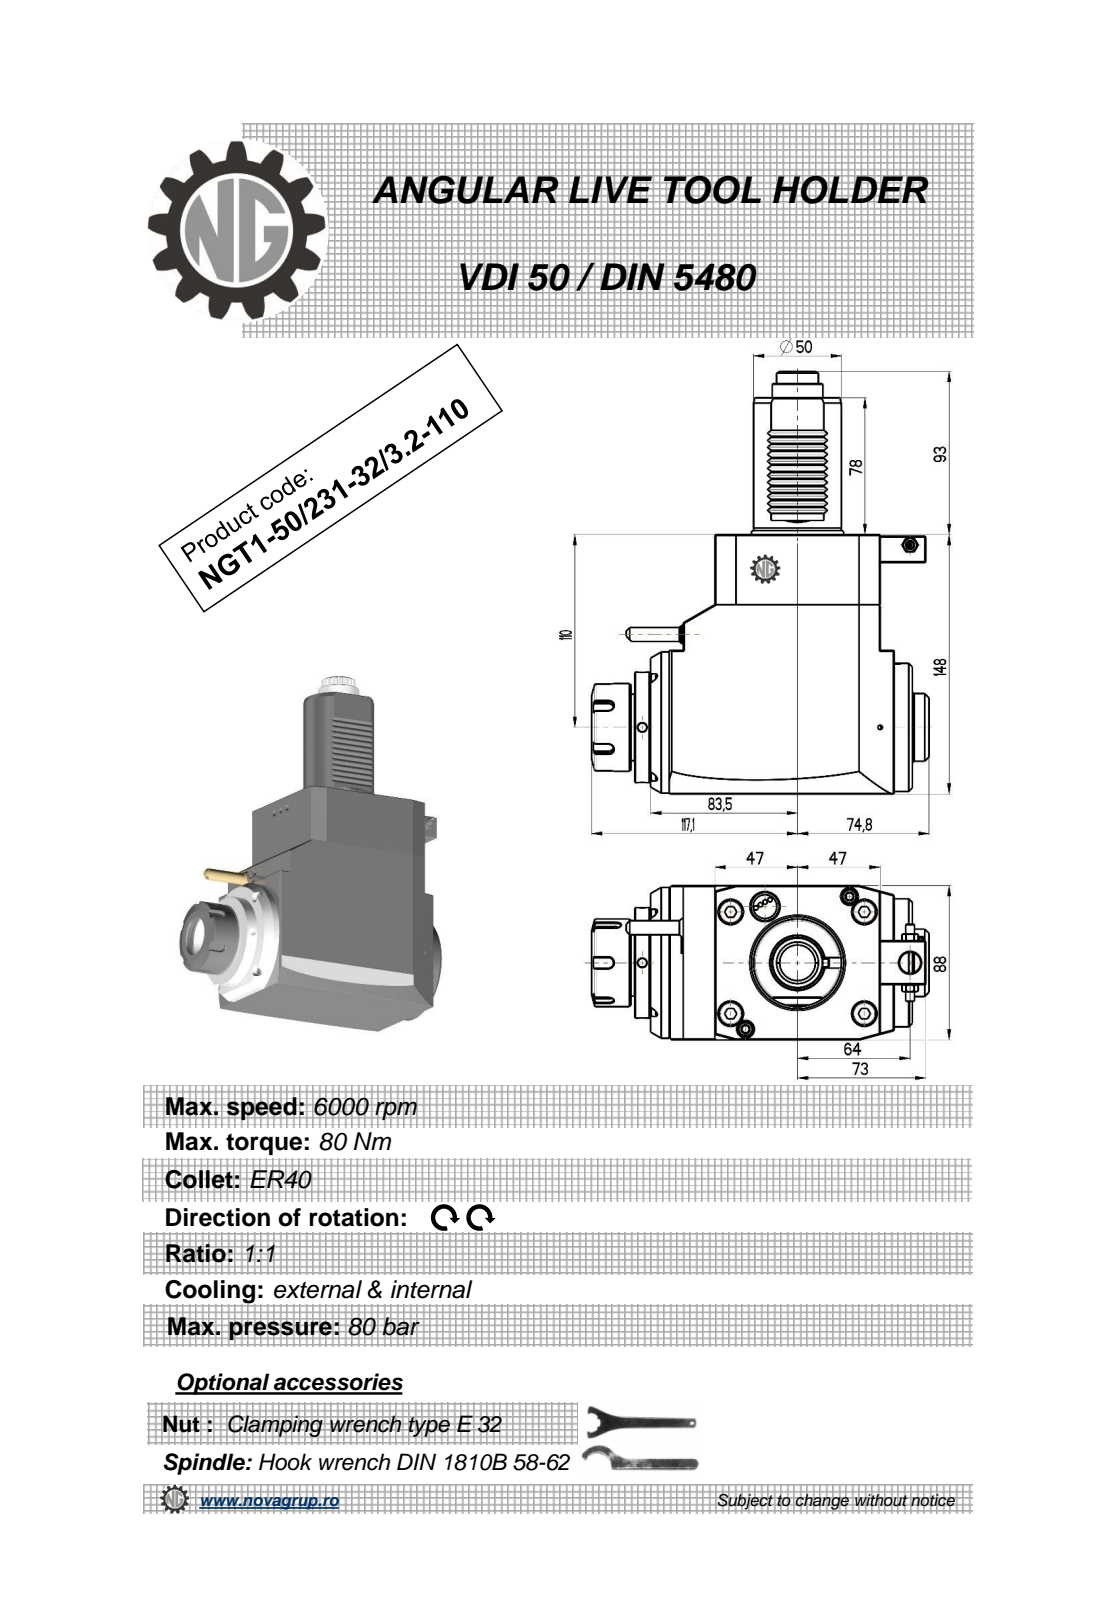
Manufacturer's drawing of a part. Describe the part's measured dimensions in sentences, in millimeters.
The part is named "NGT1_50_231_32_3_2_110". Its 3-D file was written by "PRO/ENGINEER BY PARAMETRIC TECHNOLOGY CORPORATION, 2010280 (CONFIG_CONTROL_DESIGN)". It is 1 solid with 511 faces: 195 planar, 161 cylindrical and 155 other. Overall it measures 241 by 191.9 by 88 millimeters. Its volume is 1 827 000 cubic millimeters and its surface area 113 175 square millimeters. Round holes: 3 of diameter 5, 1 of diameter 3, 1 of diameter 4.2, 1 of diameter 9.5, 1 of diameter 12, 1 of diameter 27. Round bosses or shafts: 2 of diameter 50, 1 of diameter 86, 1 of diameter 73, 1 of diameter 63, 1 of diameter 50.5, 1 of diameter 41, 1 of diameter 40, 1 of diameter 38.5. Partial cylindrical surfaces (rounded edges, fillets, slot ends): 36 of radius 3.04, 12 of radius 0.26, 12 of radius 0.3, 6 of radius 0.2, 5 of radius 3, 1 of radius 10.56, 1 of radius 11.88, 1 of radius 17.5. The main face-to-face distances are 88, 148, 94, 8, 120, 36.5, 130.5, 148.8, 112.3, 18.3. The hole center spacings are 52.46, 56.65, 101.5, 152.25, 184.38.
